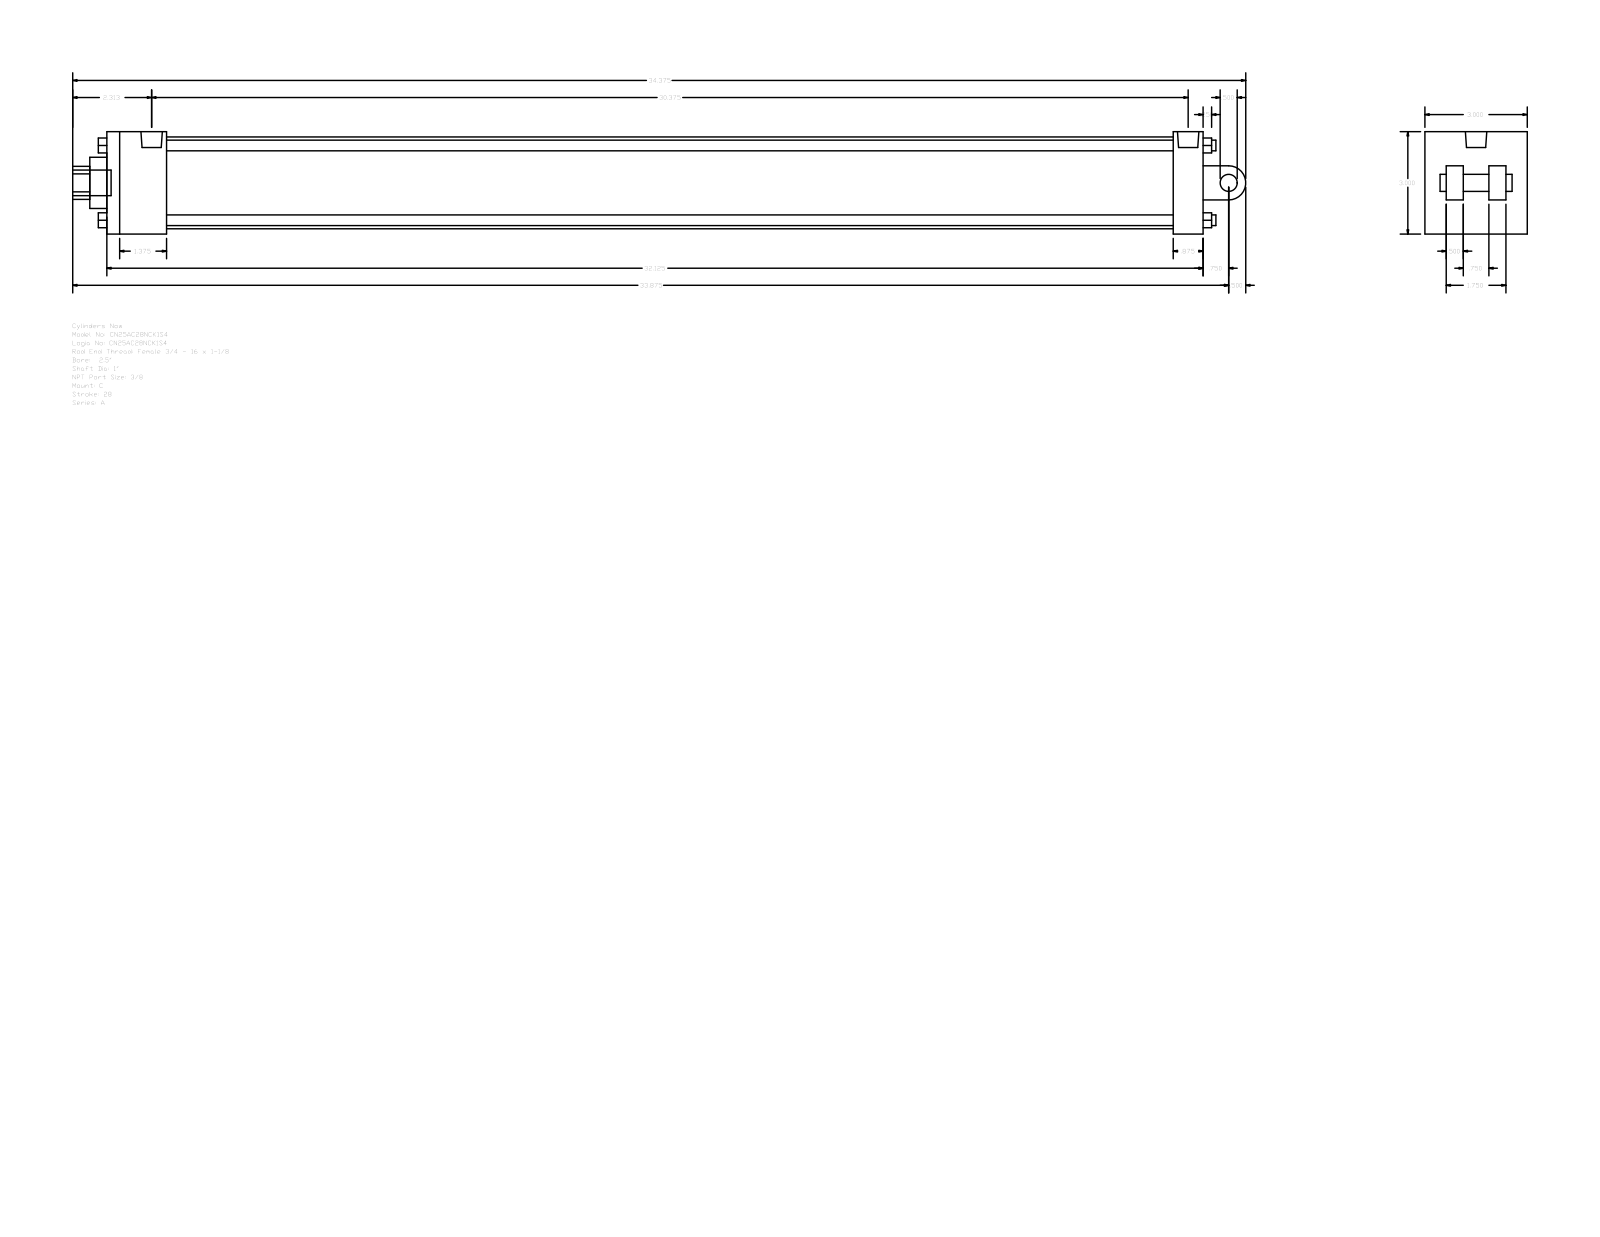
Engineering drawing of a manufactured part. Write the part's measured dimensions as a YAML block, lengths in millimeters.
part_name: "A_C__0250_1"
step_written_by: "GSSL Pune (CONFIG_CONTROL_DESIGN)"
units: millimeters
bodies: {solids: 0, faces: 135, planar: 102, cylindrical: 33, other: 0}
overall_size: [873.12, 76.2, 76.2]
round_holes:
  - {diameter: 5.56, count: 2}
  - {diameter: 15.93, count: 1}
  - {diameter: 25.4, count: 1}
  - {diameter: 38.1, count: 1}
  - {diameter: 68.33, count: 1}
round_bosses_or_shafts:
  - {diameter: 7.94, count: 4}
  - {diameter: 5.56, count: 2}
  - {diameter: 19.05, count: 1}
  - {diameter: 15.93, count: 1}
  - {diameter: 12.7, count: 1}
partial_cylinders:
  - {radius: 12.29, count: 1}
  - {radius: 12.7, count: 1}
face_to_face_distances: [76.2, 815.98, 12.7, 44.45, 793.75, 749.3, 771.53, 22.23, 15.87, 25.4]
hole_center_spacings: [2.38]
